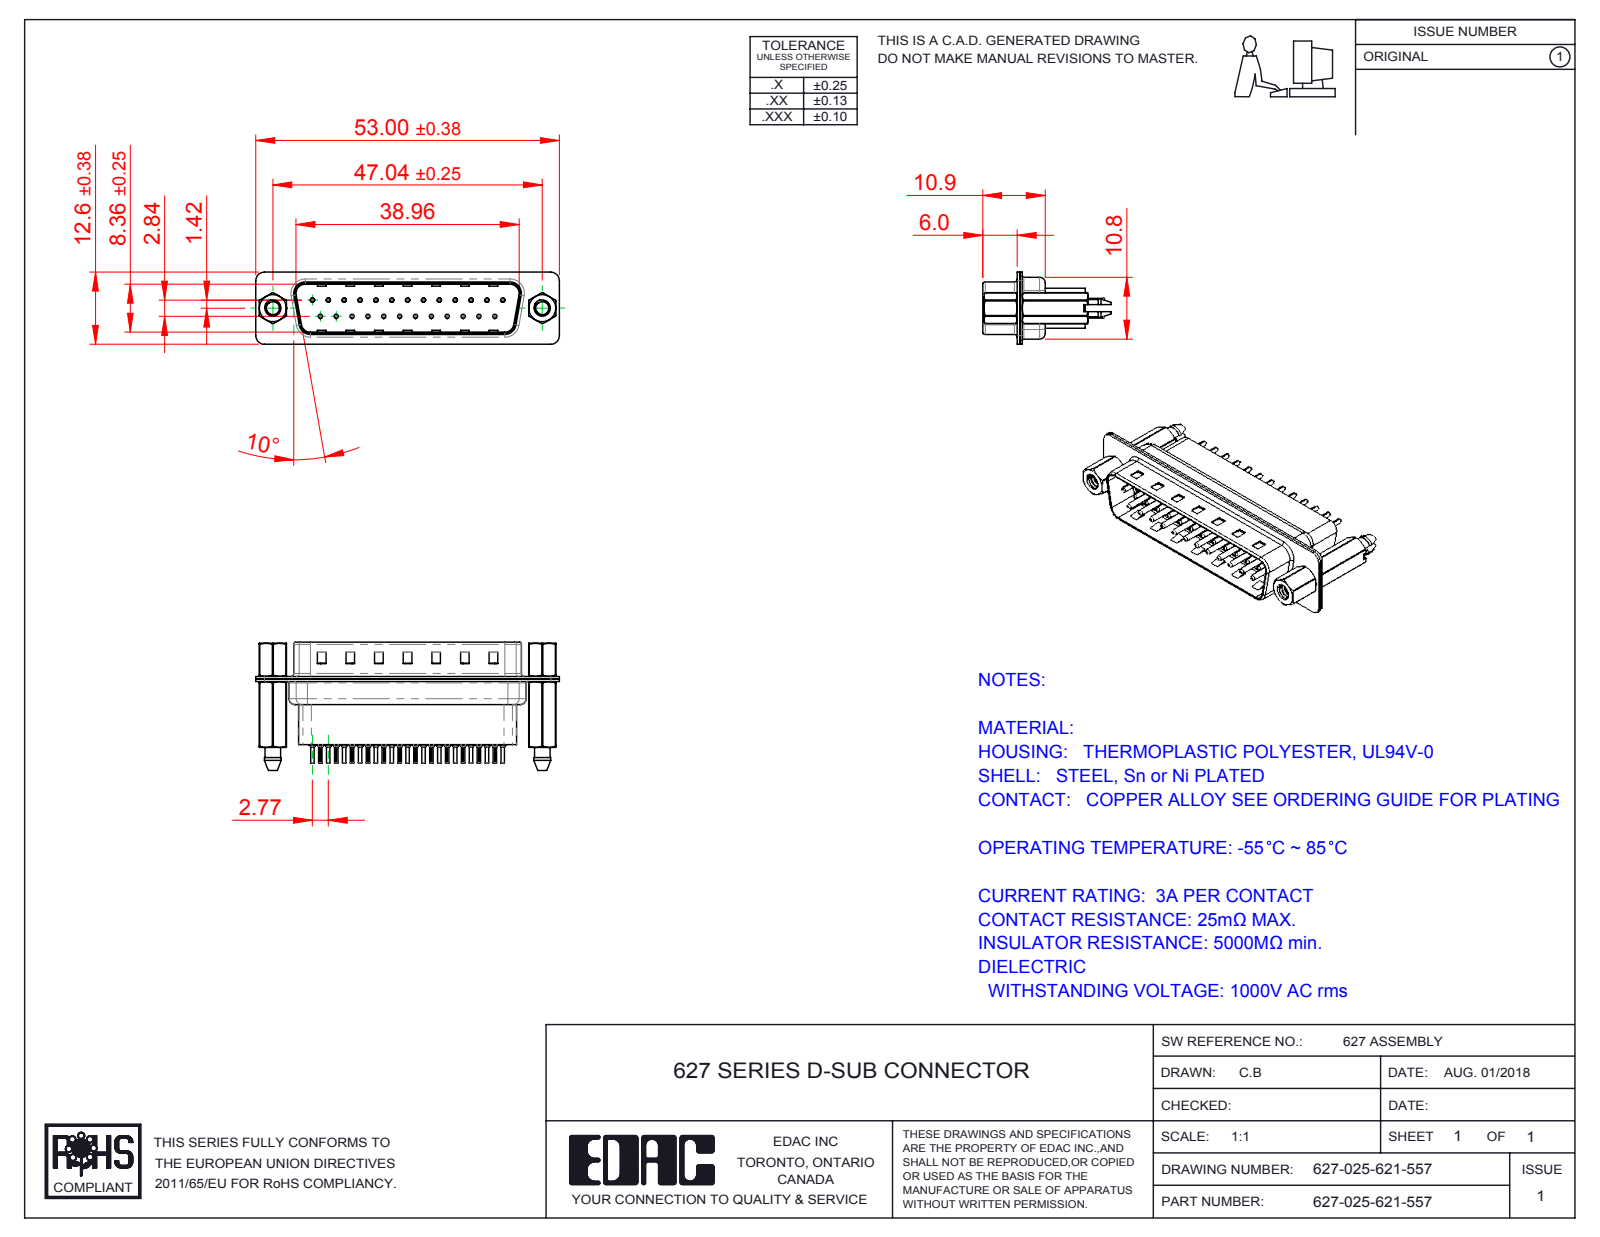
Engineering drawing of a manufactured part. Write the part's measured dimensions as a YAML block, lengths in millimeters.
part_name: "627-025-621-557; 627 Shell Front_25 Contacts; 627 4-40 Threaded Boardlock_HP; 627 4-40 Hex Standoff (+4 more)"
step_written_by: "SolidWorks 2016 (CONFIG_CONTROL_DESIGN)"
units: millimeters
bodies: {solids: 32, faces: 3060, planar: 825, cylindrical: 1200, other: 1035}
overall_size: [53, 22.4, 12.6]
volume: 4397
surface_area: 11073
round_holes:
  - {diameter: 0.2, count: 25}
  - {diameter: 0.35, count: 25}
  - {diameter: 1.1, count: 25}
  - {diameter: 1.6, count: 25}
  - {diameter: 2.26, count: 2}
  - {diameter: 2.29, count: 2}
  - {diameter: 4, count: 2}
  - {diameter: 4.8, count: 2}
round_bosses_or_shafts:
  - {diameter: 2, count: 25}
  - {diameter: 1.5, count: 25}
  - {diameter: 0.75, count: 25}
  - {diameter: 0.6, count: 25}
  - {diameter: 4.9, count: 2}
  - {diameter: 2.79, count: 2}
partial_cylinders:
  - {radius: 0.1, count: 50}
  - {radius: 1.5, count: 18}
  - {radius: 2, count: 12}
  - {radius: 1.6, count: 10}
  - {radius: 0.5, count: 8}
  - {radius: 0.25, count: 4}
  - {radius: 0.6, count: 4}
  - {radius: 0.65, count: 4}
face_to_face_distances: [0.4, 0.45, 0.82, 9.58, 0.68, 7.68, 1.5, 0.9, 1.08, 8.08]
hole_center_spacings: [3.16, 8.31, 2.77, 5.54, 11.08, 16.62, 5.03, 5.04]
